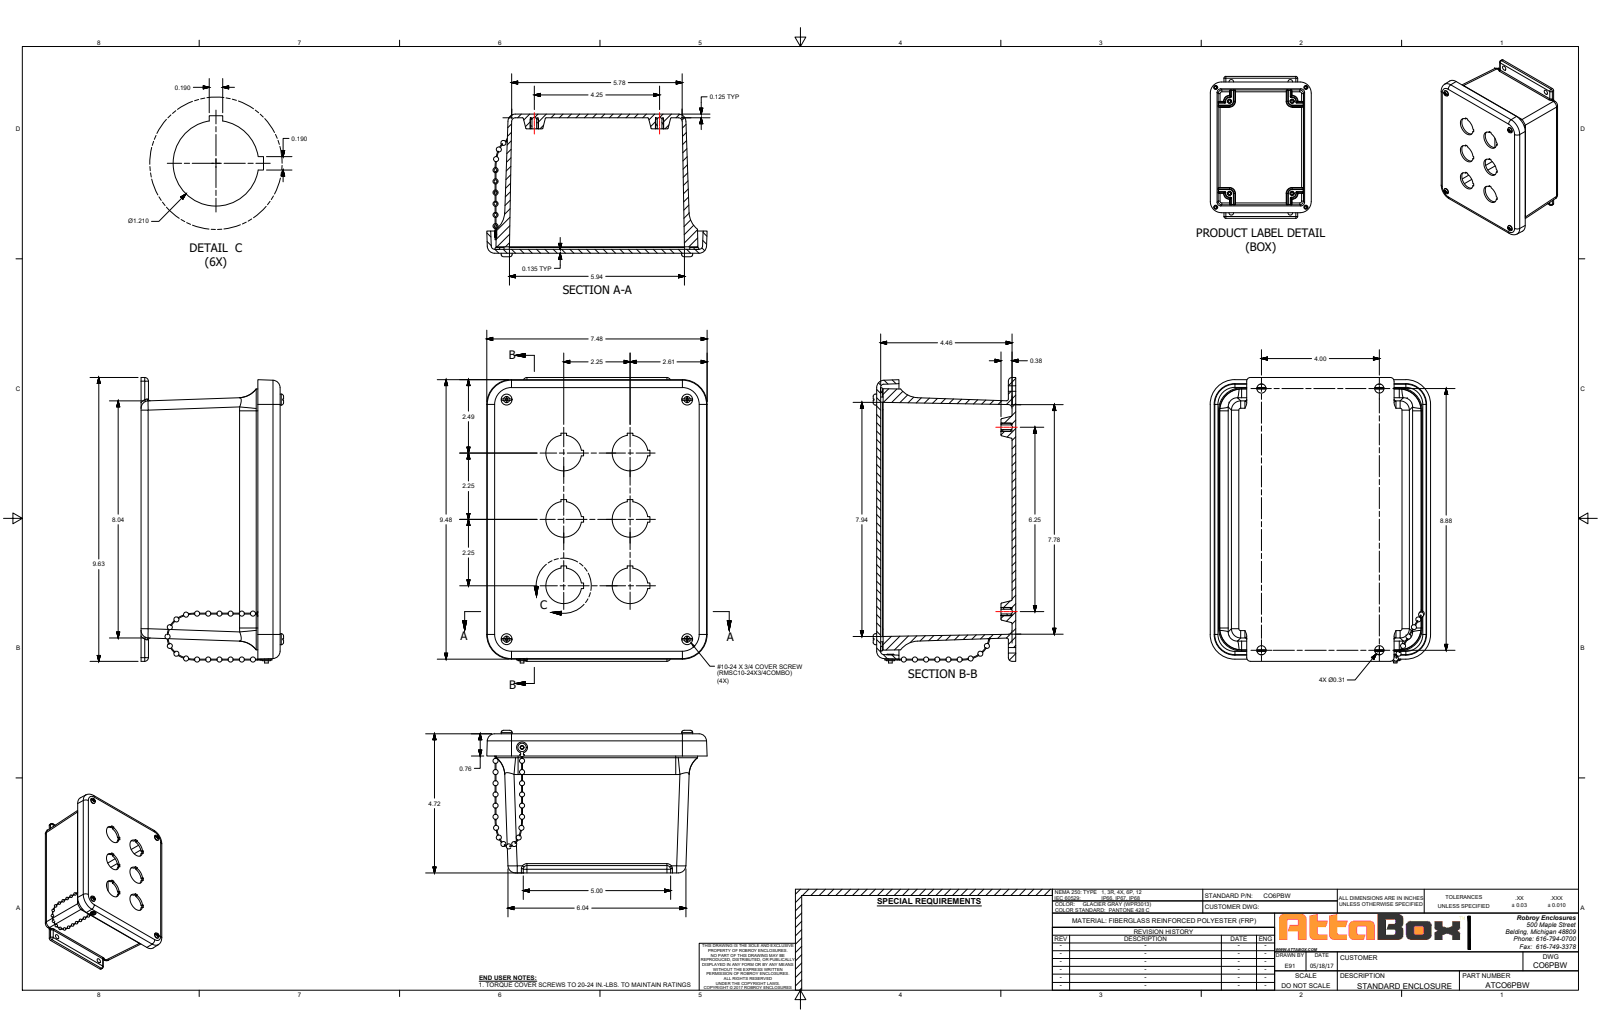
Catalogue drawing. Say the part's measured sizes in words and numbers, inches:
The part is named "CO6PBW". Its 3-D file was written by "SolidWorks 2018 (AUTOMOTIVE_DESIGN)". It is 40 solids with 635 faces: 225 planar, 211 cylindrical and 199 other. Overall it measures 9.681 by 7.476 by 4.837 inches. Its volume is 45.39 cubic inches and its surface area 562.6 square inches. Round holes: 8 of diameter 0.159, 6 of diameter 1.21, 4 of diameter 0.219, 4 of diameter 0.25, 4 of diameter 0.281, 4 of diameter 0.313, 2 of diameter 0.104, 2 of diameter 0.126, 1 of diameter 0.14. Round bosses or shafts: 8 of diameter 0.27, 4 of diameter 0.371, 4 of diameter 0.177, 2 of diameter 0.283, 2 of diameter 0.125, 2 of diameter 0.029, 1 of diameter 0.37. Partial cylindrical surfaces (rounded edges, fillets, slot ends): 36 of radius 0.031, 16 of radius 0.012, 12 of radius 0.125, 12 of radius 0.25, 8 of radius 0.033, 4 of radius 0.11, 4 of radius 0.314, 4 of radius 0.75. The main face-to-face distances are 0.135, 4.584, 4.719, 0.125, 4.459, 4.594, 4.5, 4.375, 0.084, 0.219. The hole center spacings are 2.25, 1.127, 1.318, 1.326, 1.329, 2.356, 3.182, 3.281.
